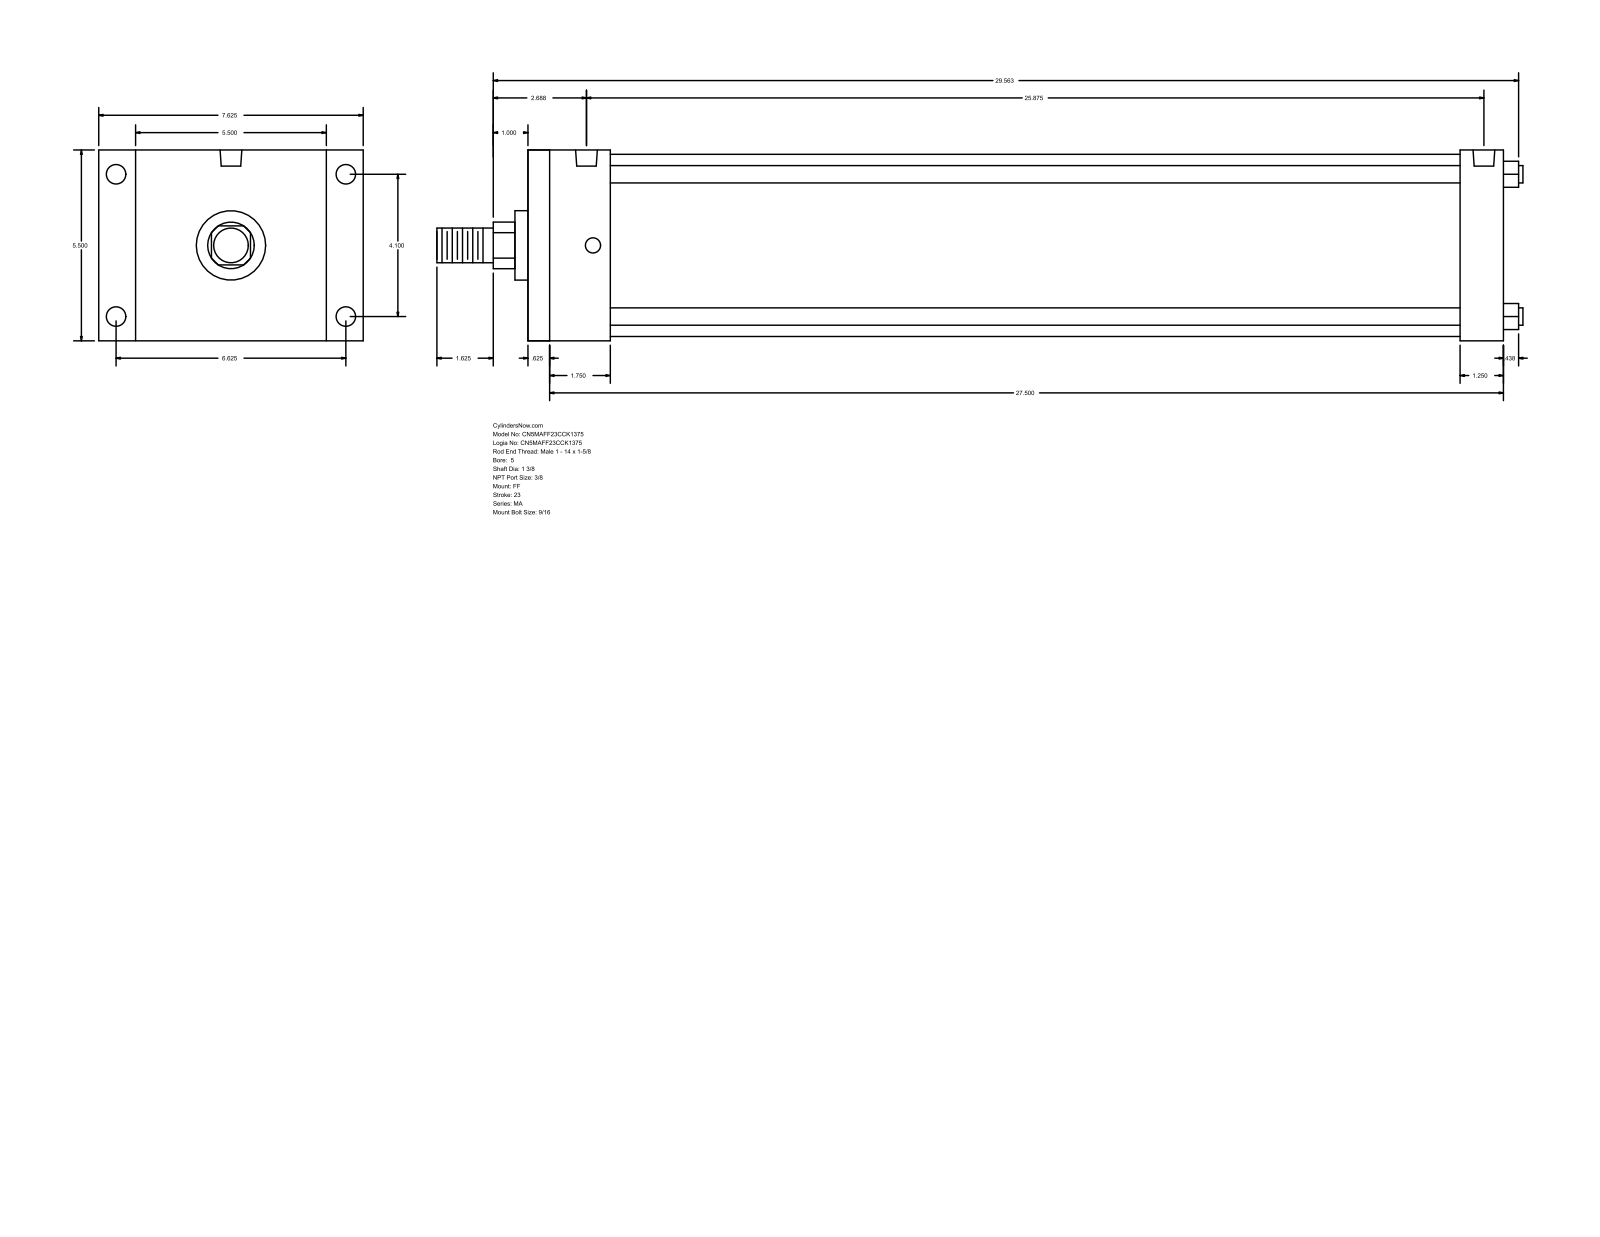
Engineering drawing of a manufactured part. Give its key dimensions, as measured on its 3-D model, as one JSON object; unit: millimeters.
{"part_name": "MA_FF__0500_1.375", "step_written_by": "GSSL Pune (CONFIG_CONTROL_DESIGN)", "units": "millimeters", "bodies": {"solids": 0, "faces": 92, "planar": 64, "cylindrical": 28, "other": 0}, "overall_size": [795.34, 193.68, 139.7], "round_holes": [[11.11, 4], [14.29, 4], [15.93, 2]], "round_bosses_or_shafts": [[12.7, 4], [133.35, 1], [50.8, 1], [34.92, 1], [25.4, 1]], "partial_cylinders_radius": [[17.06, 1]], "face_to_face_distances": [139.7, 714.37, 15.87, 698.5, 682.62, 666.75, 31.75, 60.32, 44.45, 622.3], "hole_center_spacings": [104.14, 168.28, 197.9, 647.7, 4.76, 4.77, 652.46, 652.47]}
